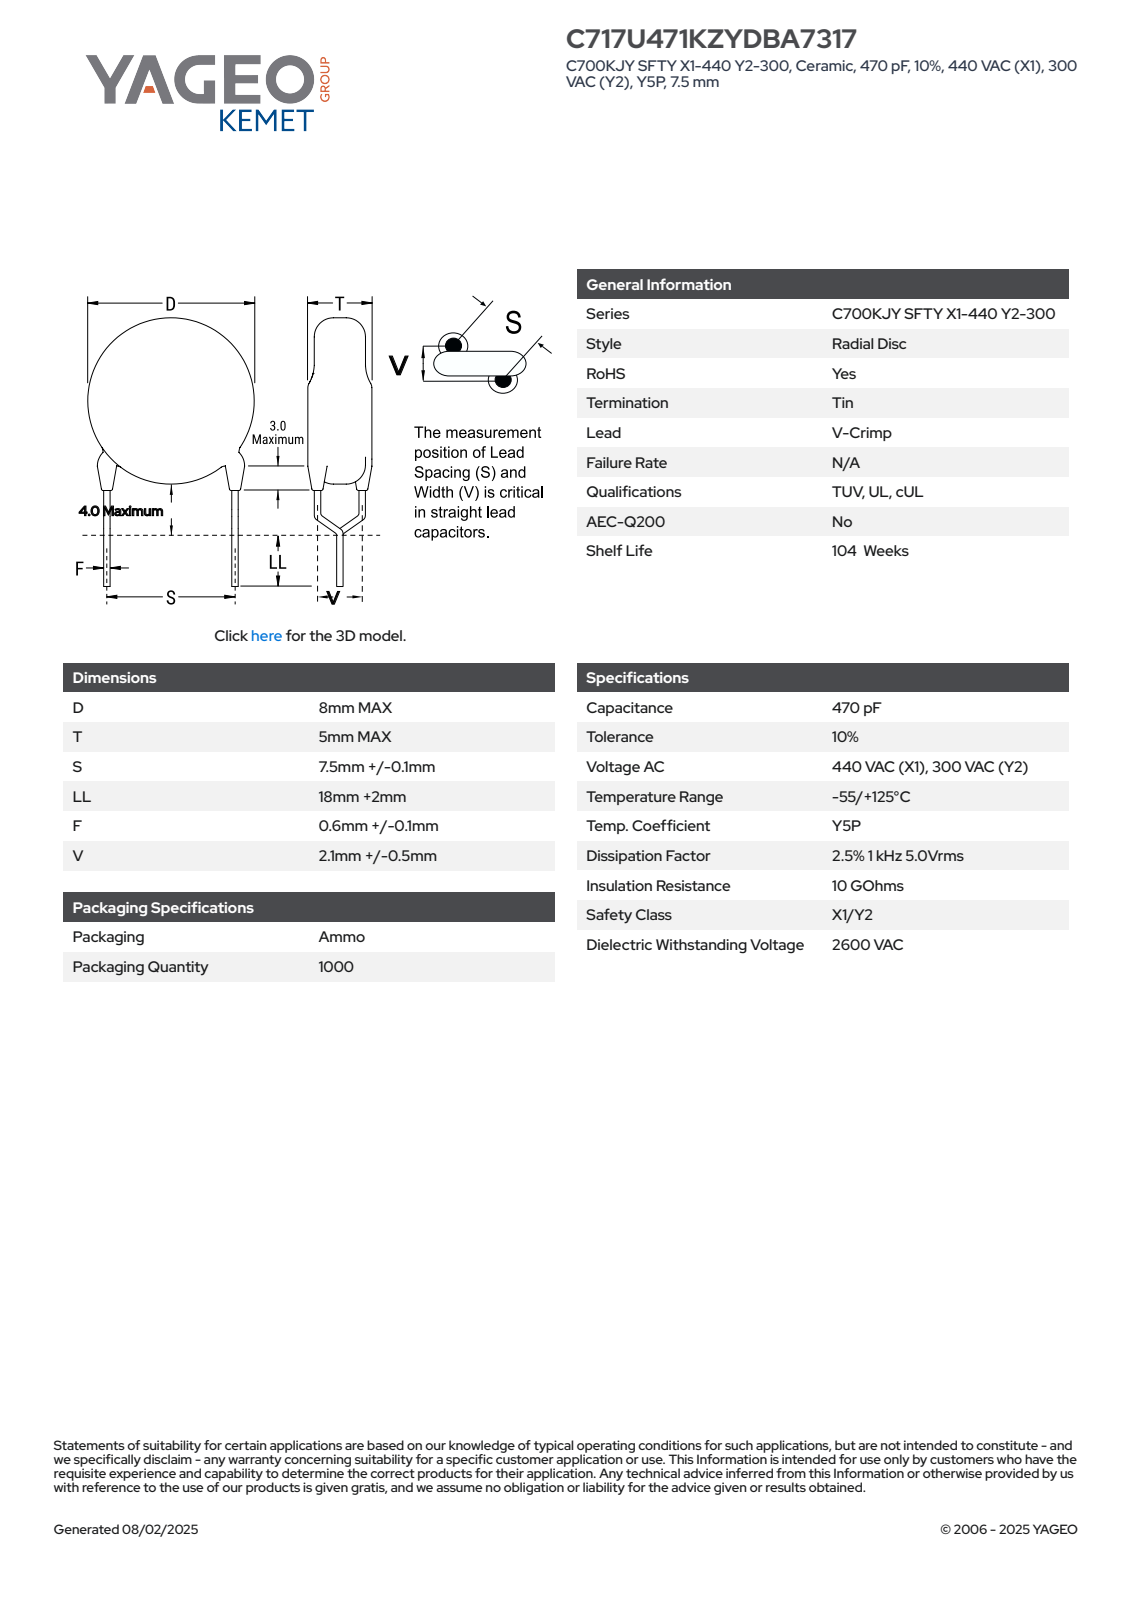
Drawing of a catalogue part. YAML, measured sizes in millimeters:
part_name: "CCD_VC8X5_D8T5S7.5LL20F0.7V2.1"
step_written_by: "SolidWorks 2021 (AUTOMOTIVE_DESIGN)"
units: millimeters
bodies: {solids: 4, faces: 89, planar: 63, cylindrical: 22, other: 4}
overall_size: [28, 8.7, 5]
volume: 261
surface_area: 313
round_bosses_or_shafts:
  - {diameter: 0.7, count: 6}
  - {diameter: 1.2, count: 4}
  - {diameter: 8, count: 1}
face_to_face_distances: [5, 20, 0.97, 24.63, 4.63, 23.66, 3.66, 0.36, 0.78, 0.35]
